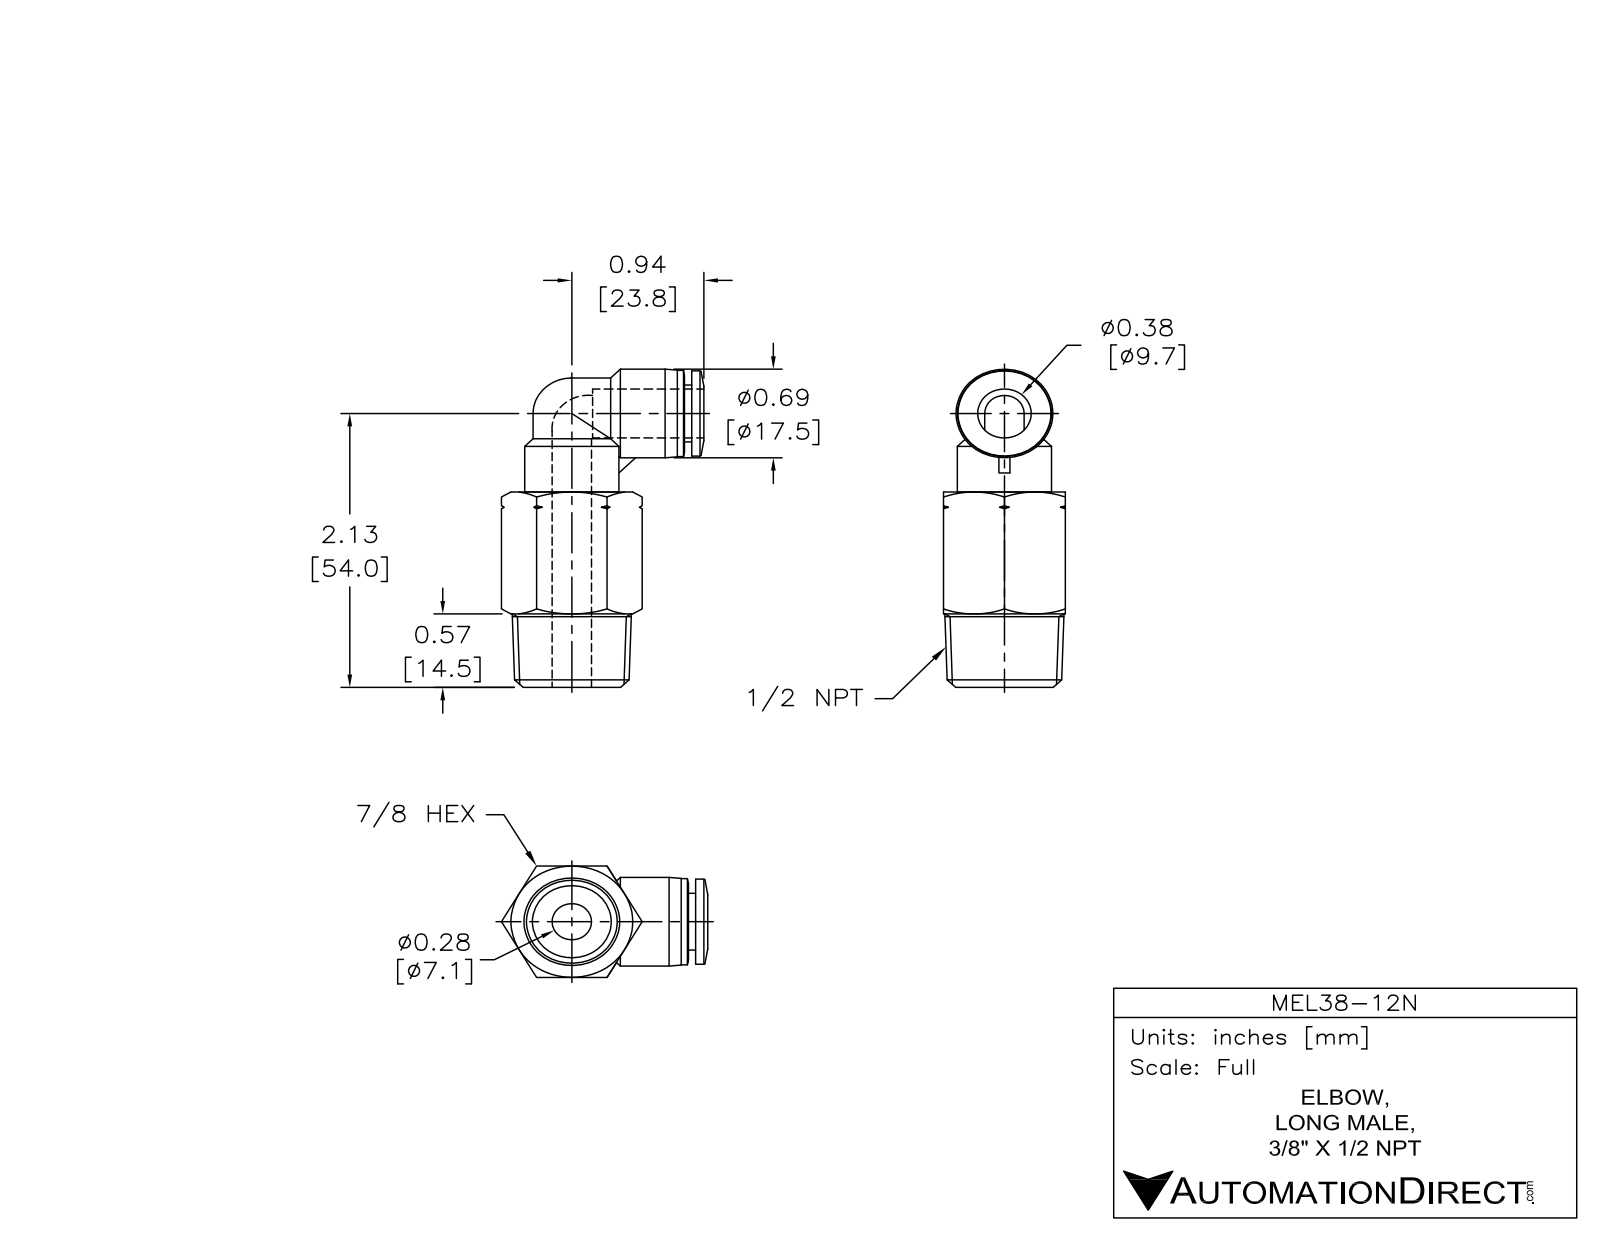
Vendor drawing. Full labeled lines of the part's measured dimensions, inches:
Part name (STEP PRODUCT): MEL38-12N
STEP written by: SolidWorks 2015 (AUTOMOTIVE_DESIGN)
Units: inches
Bodies: 1 solid, 87 faces (16 planar, 20 cylindrical, 51 other)
Overall size (bounding box): 2.47 × 1.467 × 0.866
Volume: 1.17 in³ · Surface area: 11.66 in²
Round holes (diameter × count): ⌀0.276 ×2, ⌀0.386 ×1
Round bosses / shafts (diameter × count): ⌀0.669 ×2, ⌀0.689 ×1, ⌀0.661 ×1, ⌀0.551 ×1, ⌀0.441 ×1
Partial cylindrical surfaces — rounded edges, fillets, slot ends (radius × count): R0.276 ×1
Main face-to-face distances: 0.866, 1.516, 0.051, 0.654, 0.705, 0.571, 0.945, 0.394, 0.472, 0.079
